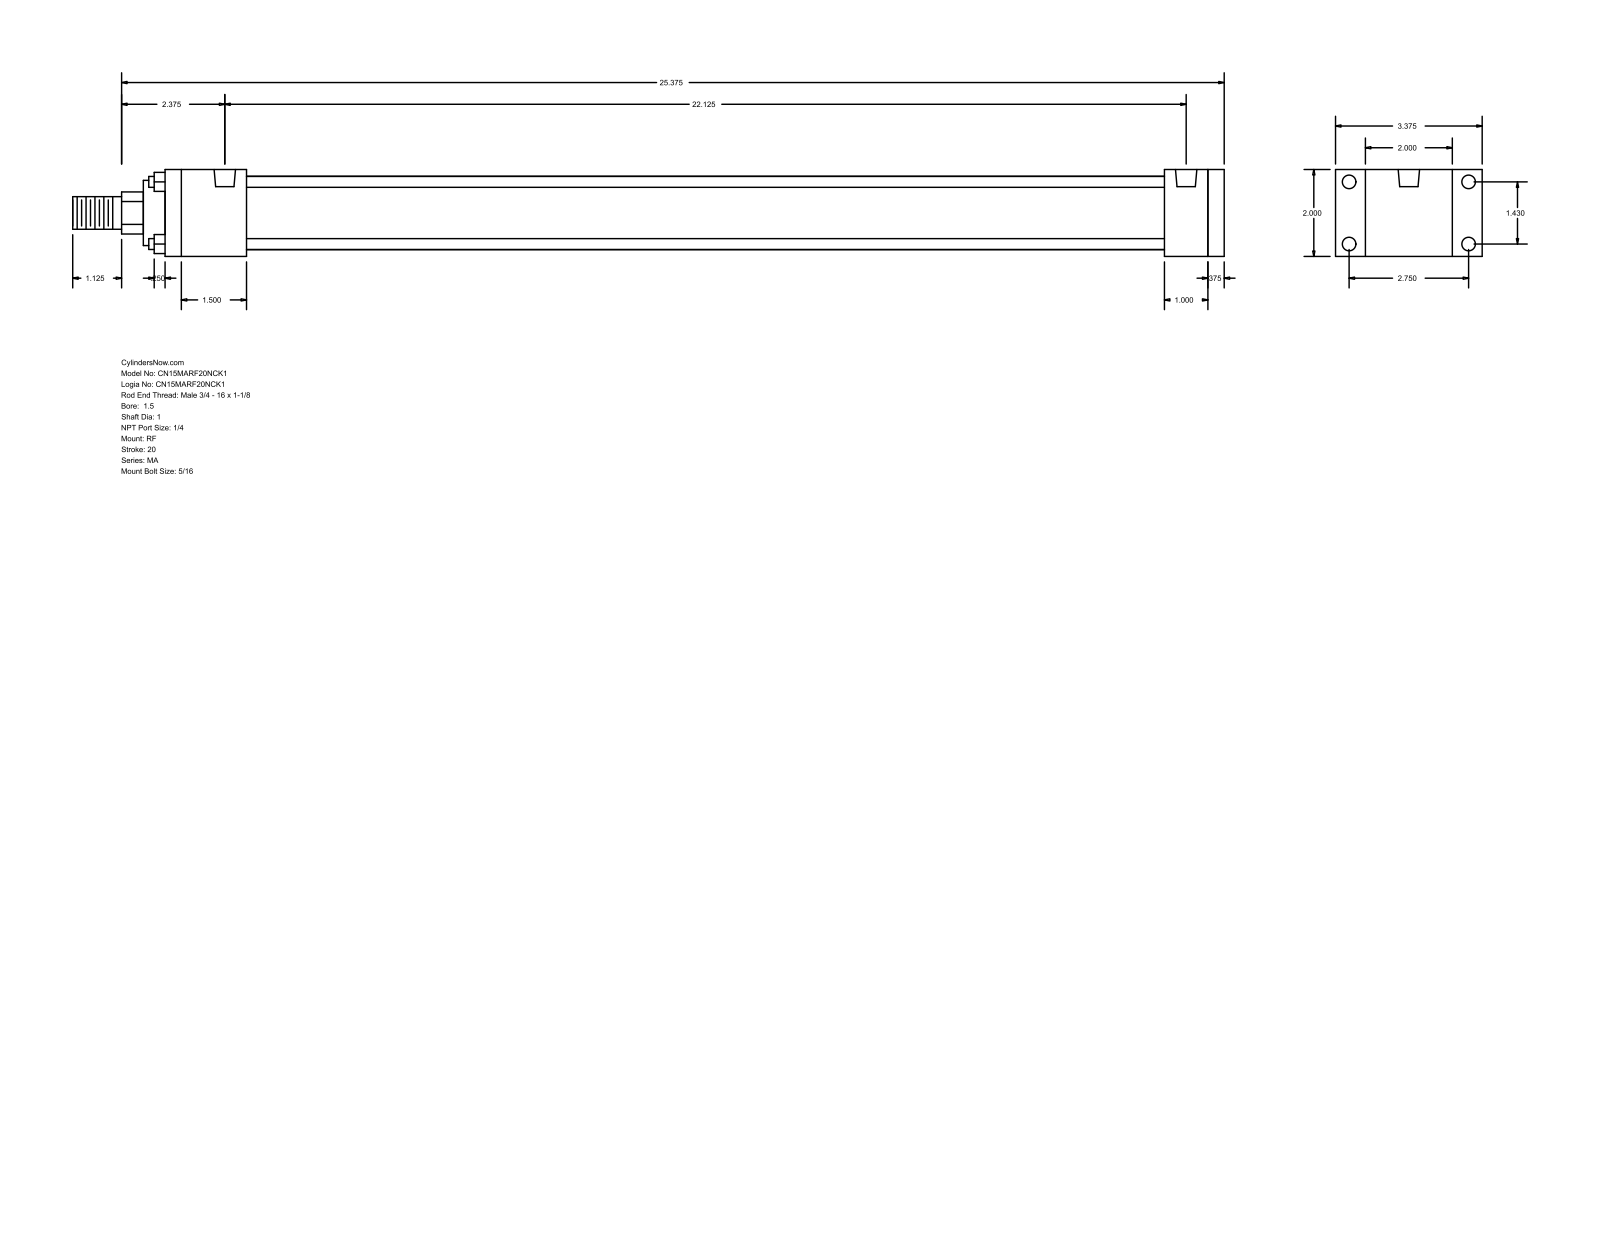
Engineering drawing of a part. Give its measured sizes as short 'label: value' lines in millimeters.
name: MA_RF__0150_1
written by: GSSL Pune (CONFIG_CONTROL_DESIGN)
unit: mm
bodies: 0 solids, 92 faces (64 planar, 28 cylindrical, 0 other)
size: 673.1 × 85.72 × 50.8
holes: 8× ⌀7.94, 2× ⌀12.49
bosses: 4× ⌀6.35, 1× ⌀42.93, 1× ⌀38.1, 1× ⌀25.4, 1× ⌀19.05
rounds: 1× R12.29
face distances: 50.8, 9.52, 619.12, 609.6, 25.4, 584.2, 34.92, 47.63, 536.57, 561.97
hole spacings: 36.32, 69.84, 78.72, 561.97
